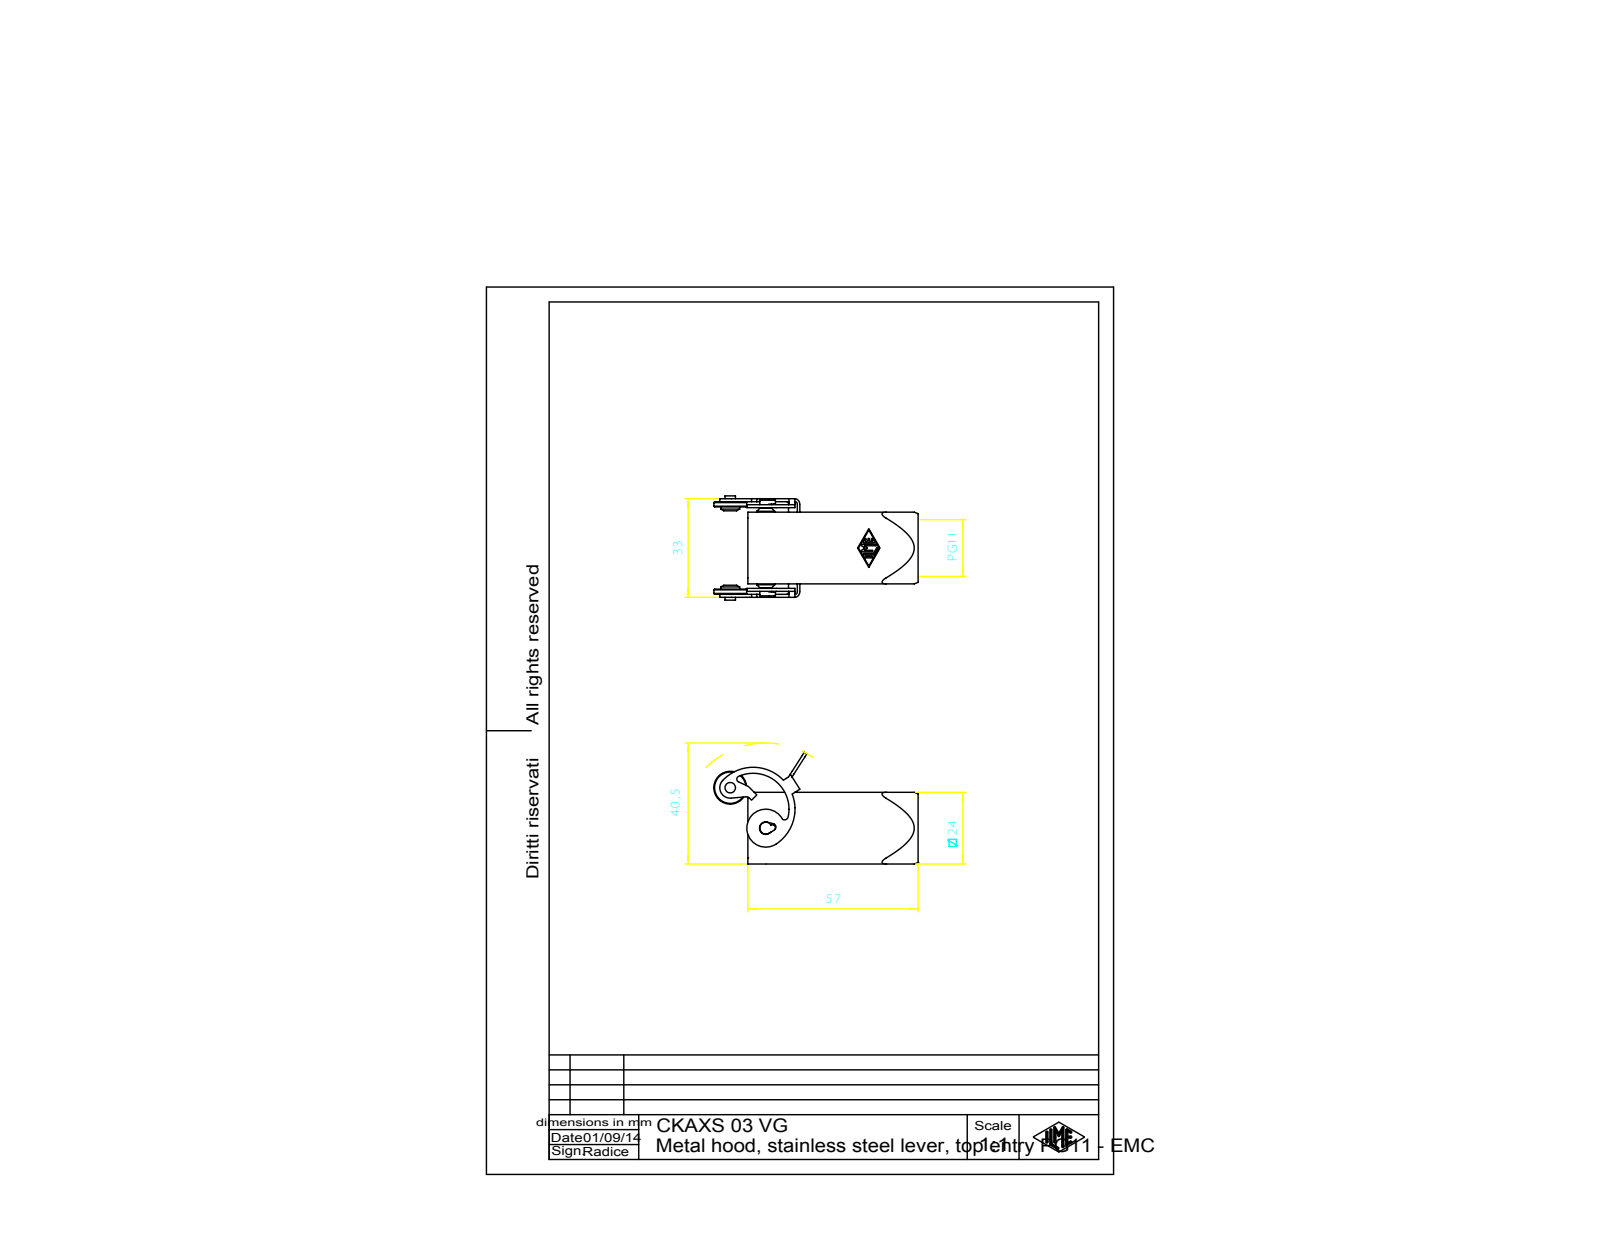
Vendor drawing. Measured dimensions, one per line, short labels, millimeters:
name: CKAXS 03 VG
written by: Autodesk Inventor 7 (AUTOMOTIVE_DESIGN)
unit: mm
bodies: 2 solids, 237 faces (81 planar, 90 cylindrical, 66 other)
size: 62.9 × 37.42 × 34.9
volume: 8 845 mm³; area: 12 105 mm²
holes: 1× ⌀3.3, 1× ⌀15, 1× ⌀17.26
bosses: 1× ⌀11, 1× ⌀6.3, 1× ⌀6, 1× ⌀4, 1× ⌀3.5
rounds: 18× R2, 14× R0.25, 6× R1, 2× R0.8, 1× R1.1, 1× R1.25, 1× R1.5, 1× R2.1
face distances: 1, 23, 24, 22, 2, 3, 2.5, 25.5, 3.5, 26.5
